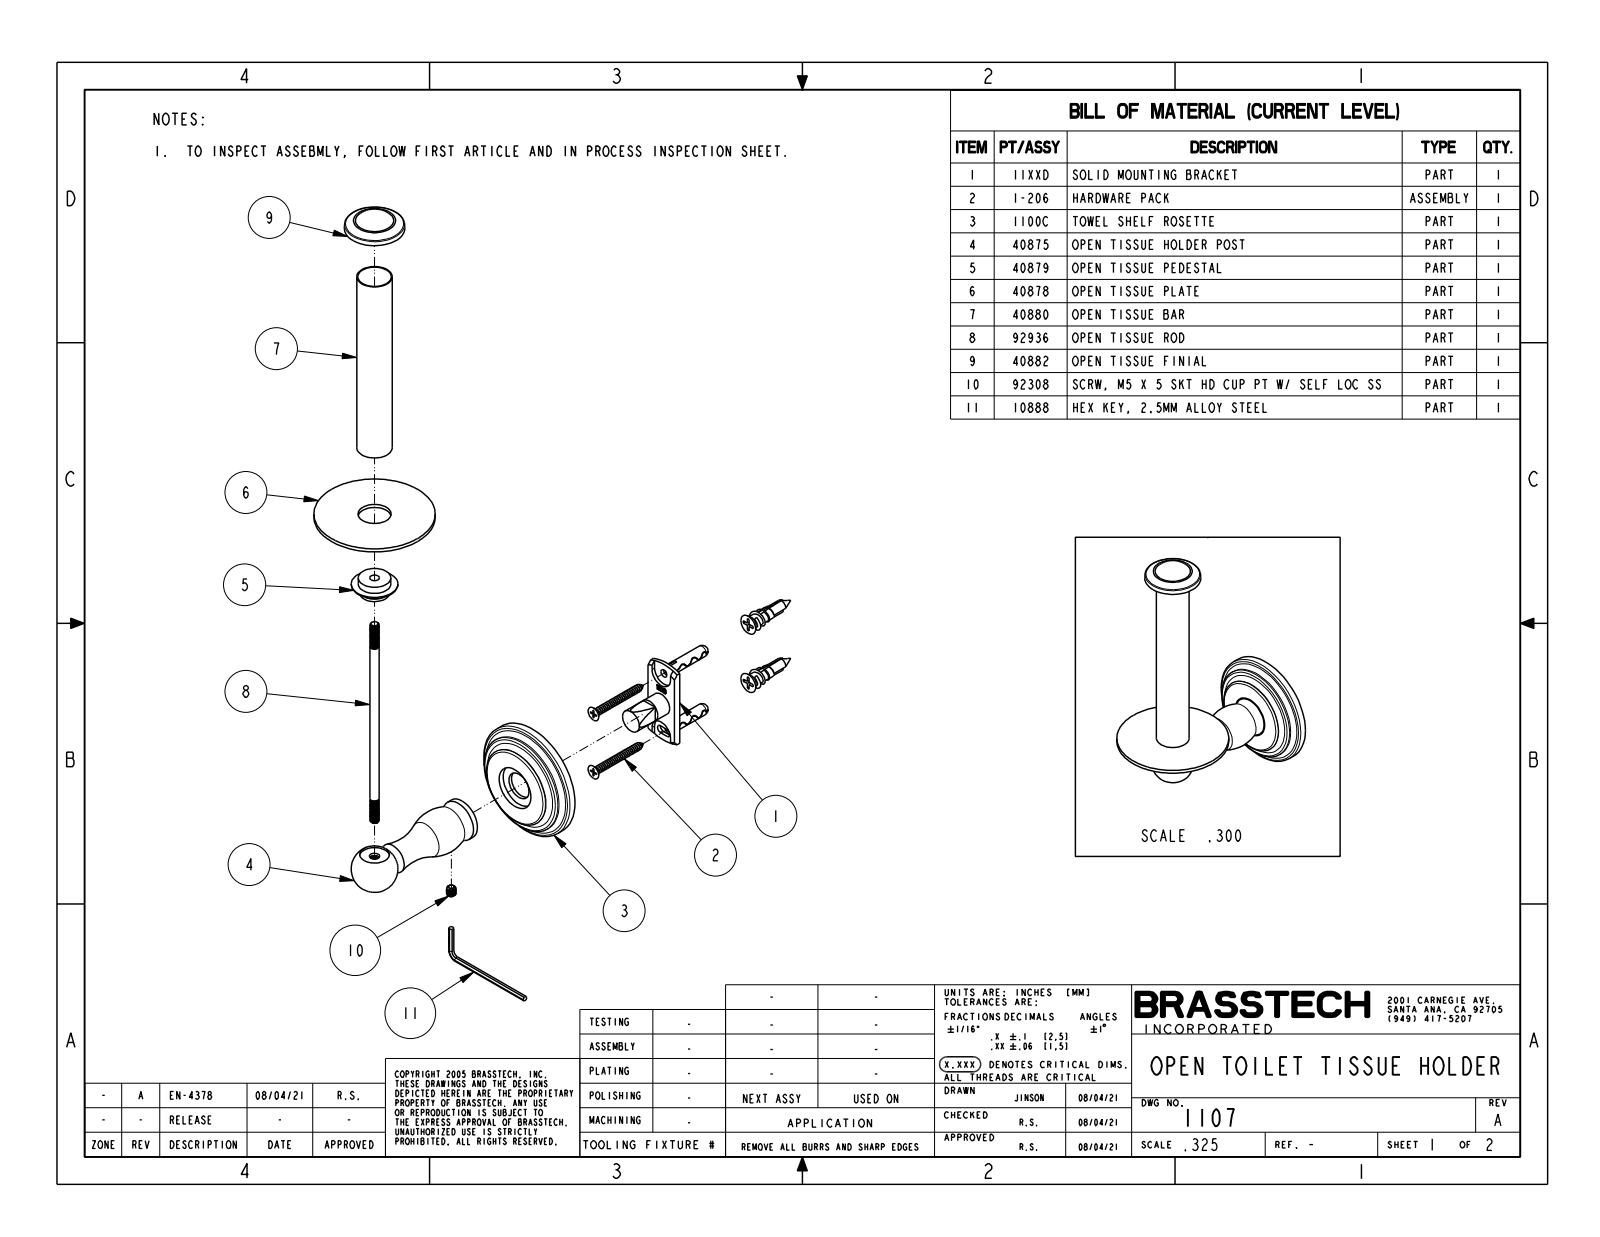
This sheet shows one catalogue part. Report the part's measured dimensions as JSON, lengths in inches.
{"part_name": "1107", "step_written_by": "CREO PARAMETRIC BY PTC INC, 2018400 (CONFIG_CONTROL_DESIGN)", "units": "inches", "bodies": {"solids": 1, "faces": 56, "planar": 8, "cylindrical": 14, "other": 34}, "overall_size": [6.792, 4.291, 2.56], "volume_in3": 6.193, "surface_area_in2": 43.49, "round_holes": [[0.63, 1]], "round_bosses_or_shafts": [[2.56, 1], [2.559, 1], [2.182, 1], [1.748, 1], [0.748, 1], [0.626, 1]], "face_to_face_distances": [0.079, 0.512, 0.362, 0.15, 0.189, 0.173, 0.323, 4.765, 4.686, 0.206]}
